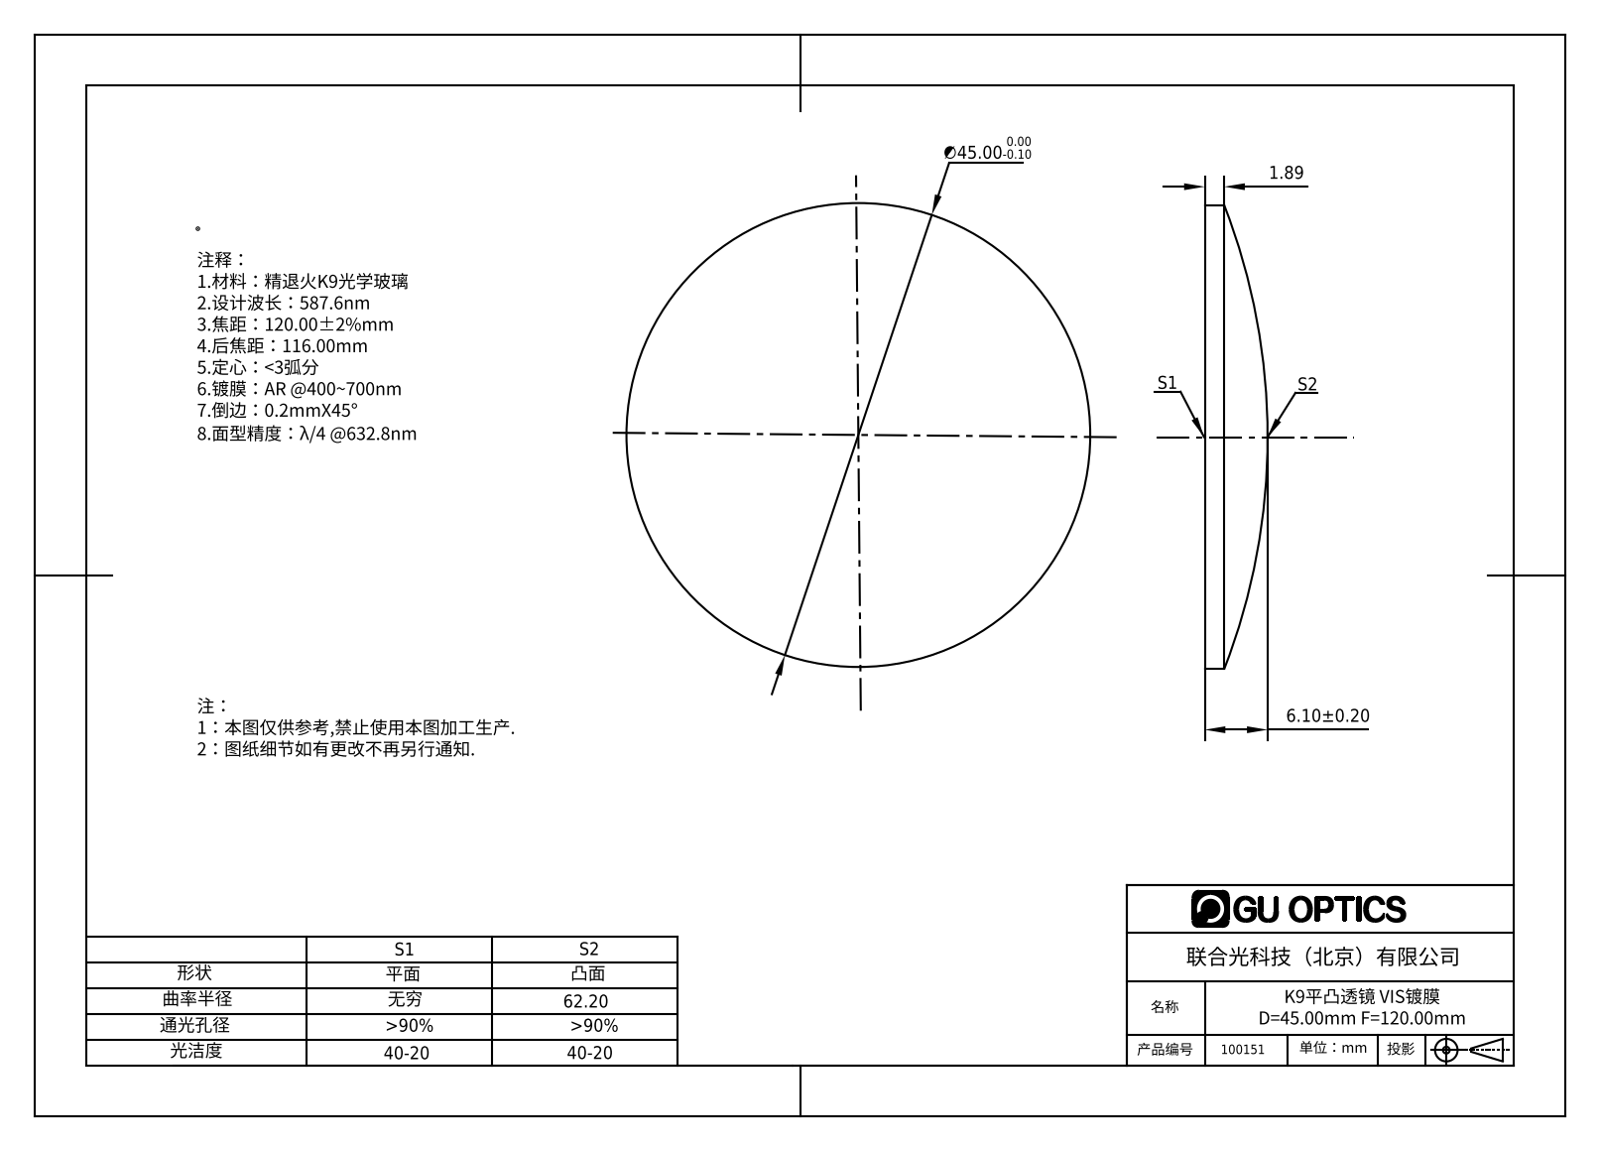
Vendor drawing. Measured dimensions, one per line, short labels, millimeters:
name: 100151
written by: SolidWorks 2016 (AUTOMOTIVE_DESIGN)
unit: mm
bodies: 1 solid, 5 faces (1 planar, 2 cylindrical, 2 other)
size: 45 × 45 × 6.1
volume: 6 393 mm³; area: 3 504 mm²
bosses: 1× ⌀45
